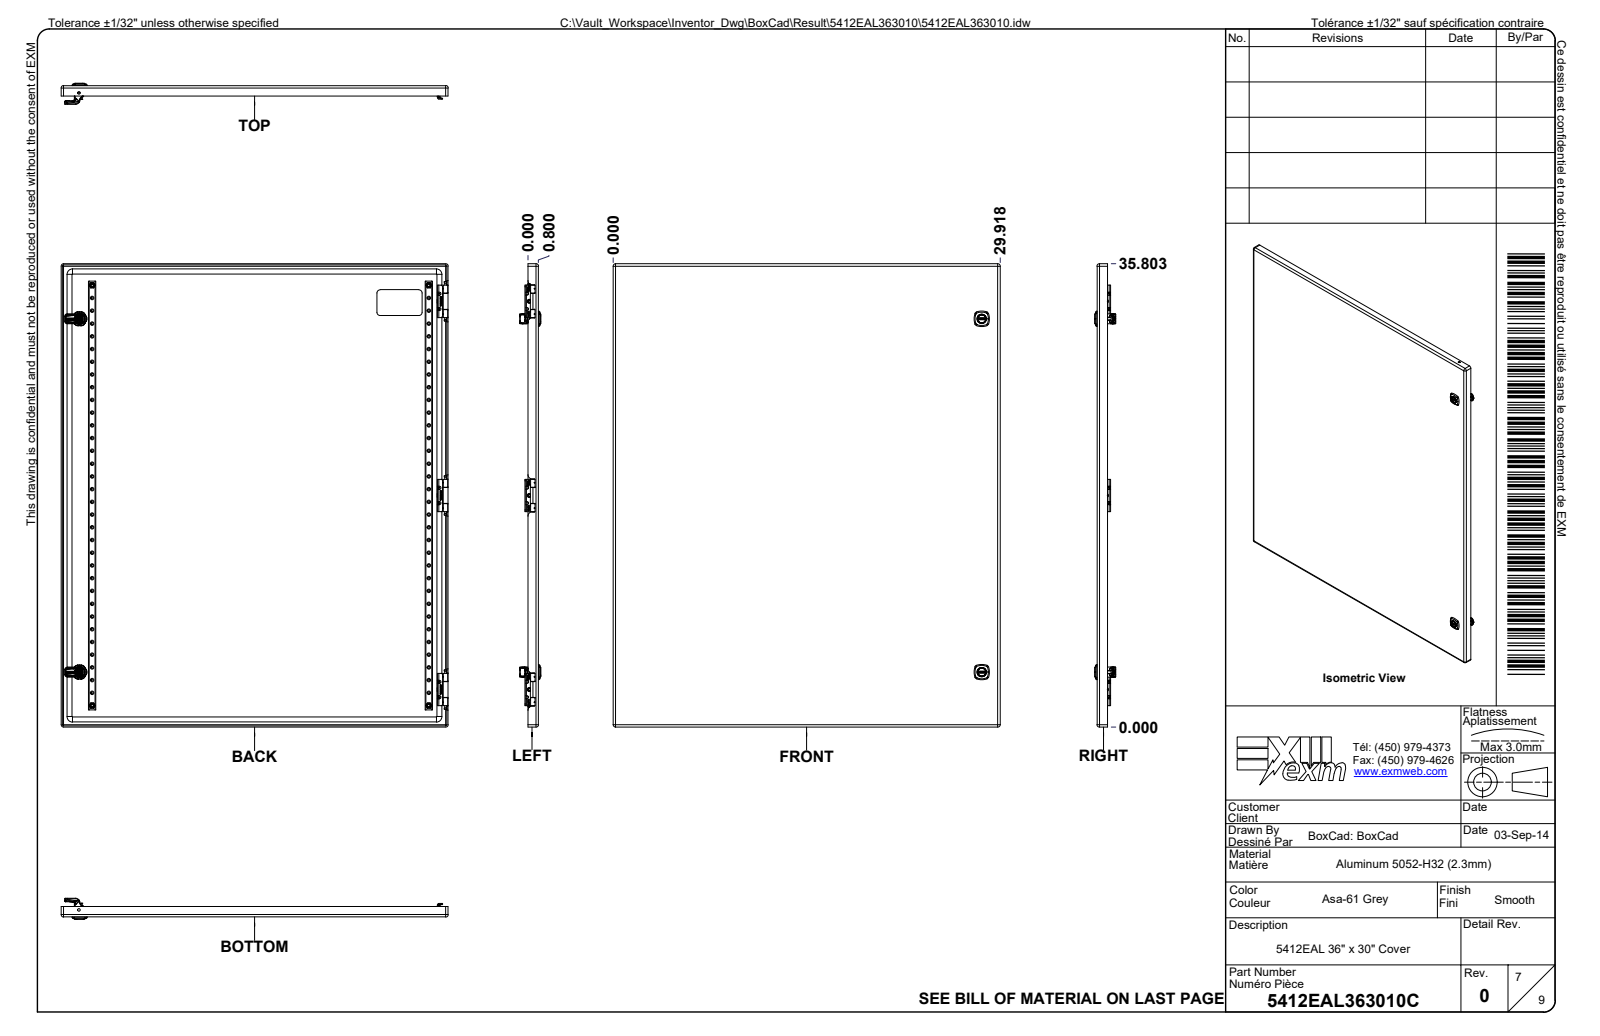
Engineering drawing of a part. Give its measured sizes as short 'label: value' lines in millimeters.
name: 5412EAL363010; 5412EAL363010B; 5412EAL363010B-P; STK-Q-16010 (+8 more)
written by: Autodesk Inventor 2024 (AUTOMOTIVE_DESIGN)
unit: mm
bodies: 78 solids, 7294 faces (3463 planar, 1476 cylindrical, 2355 other)
size: 914.4 × 763.1 × 285.5
volume: 7 590 000 mm³; area: 6 509 000 mm²
holes: 64× ⌀4.2, 11× ⌀0.8, 9× ⌀5.1, 8× ⌀8, 7× ⌀7.4, 6× ⌀1.1, 6× ⌀6.9, 6× ⌀7.9, 6× ⌀12.7, 4× ⌀5, 4× ⌀6.8, 4× ⌀9.9
bosses: 64× ⌀6, 12× ⌀1, 11× ⌀0.8, 10× ⌀5.9, 6× ⌀7.9, 4× ⌀18.2, 4× ⌀9.5, 3× ⌀12
rounds: 106× R0.5, 94× R1, 86× R0.2, 50× R0.3, 38× R0.8, 29× R3.2, 28× R0.3, 24× R3.1
face distances: 2.3, 278.8, 276.6, 281.1, 24.5, 22.2, 254.4, 256.6, 2.7, 27.2
hole spacings: 50, 25, 75, 100, 125, 150, 175, 200
